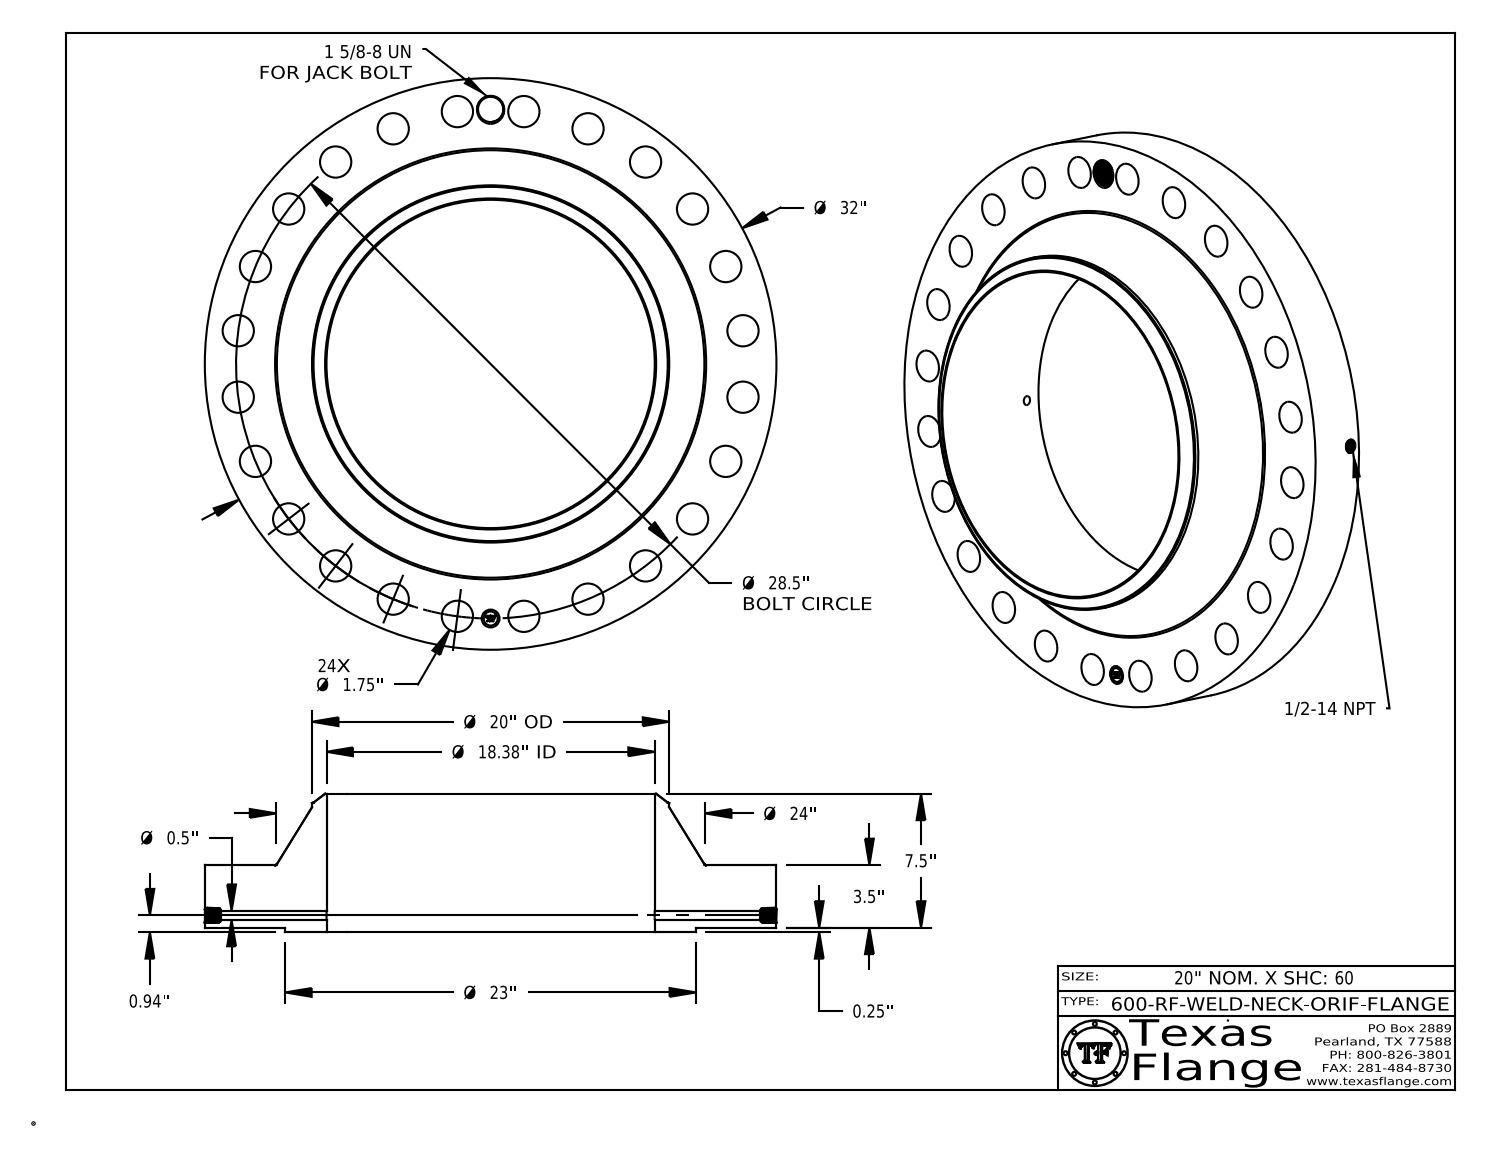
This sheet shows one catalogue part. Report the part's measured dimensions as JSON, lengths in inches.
{"part_name": "600-RF-WELD-NECK", "step_written_by": "CATIA V5 STEP AP214 (AUTOMOTIVE_DESIGN)", "units": "inches", "bodies": {"solids": 1, "faces": 883, "planar": 369, "cylindrical": 151, "other": 363}, "overall_size": [32, 32, 7.75], "volume_in3": 2113, "surface_area_in2": 2446, "round_holes": [[1.75, 24], [0.5, 1], [0.672, 1], [1, 1], [1.409, 1], [18.376, 1]], "round_bosses_or_shafts": [[0.061, 8], [32, 1], [23, 1], [20, 1], [0.788, 1]], "face_to_face_distances": [3.5, 0.25, 3.75, 7.75, 7.5, 4, 3.735, 3.485, 0.015, 4.015], "hole_center_spacings": [14.25, 17.35, 24.681, 28.256, 10.906, 3.72, 7.376, 20.152]}
